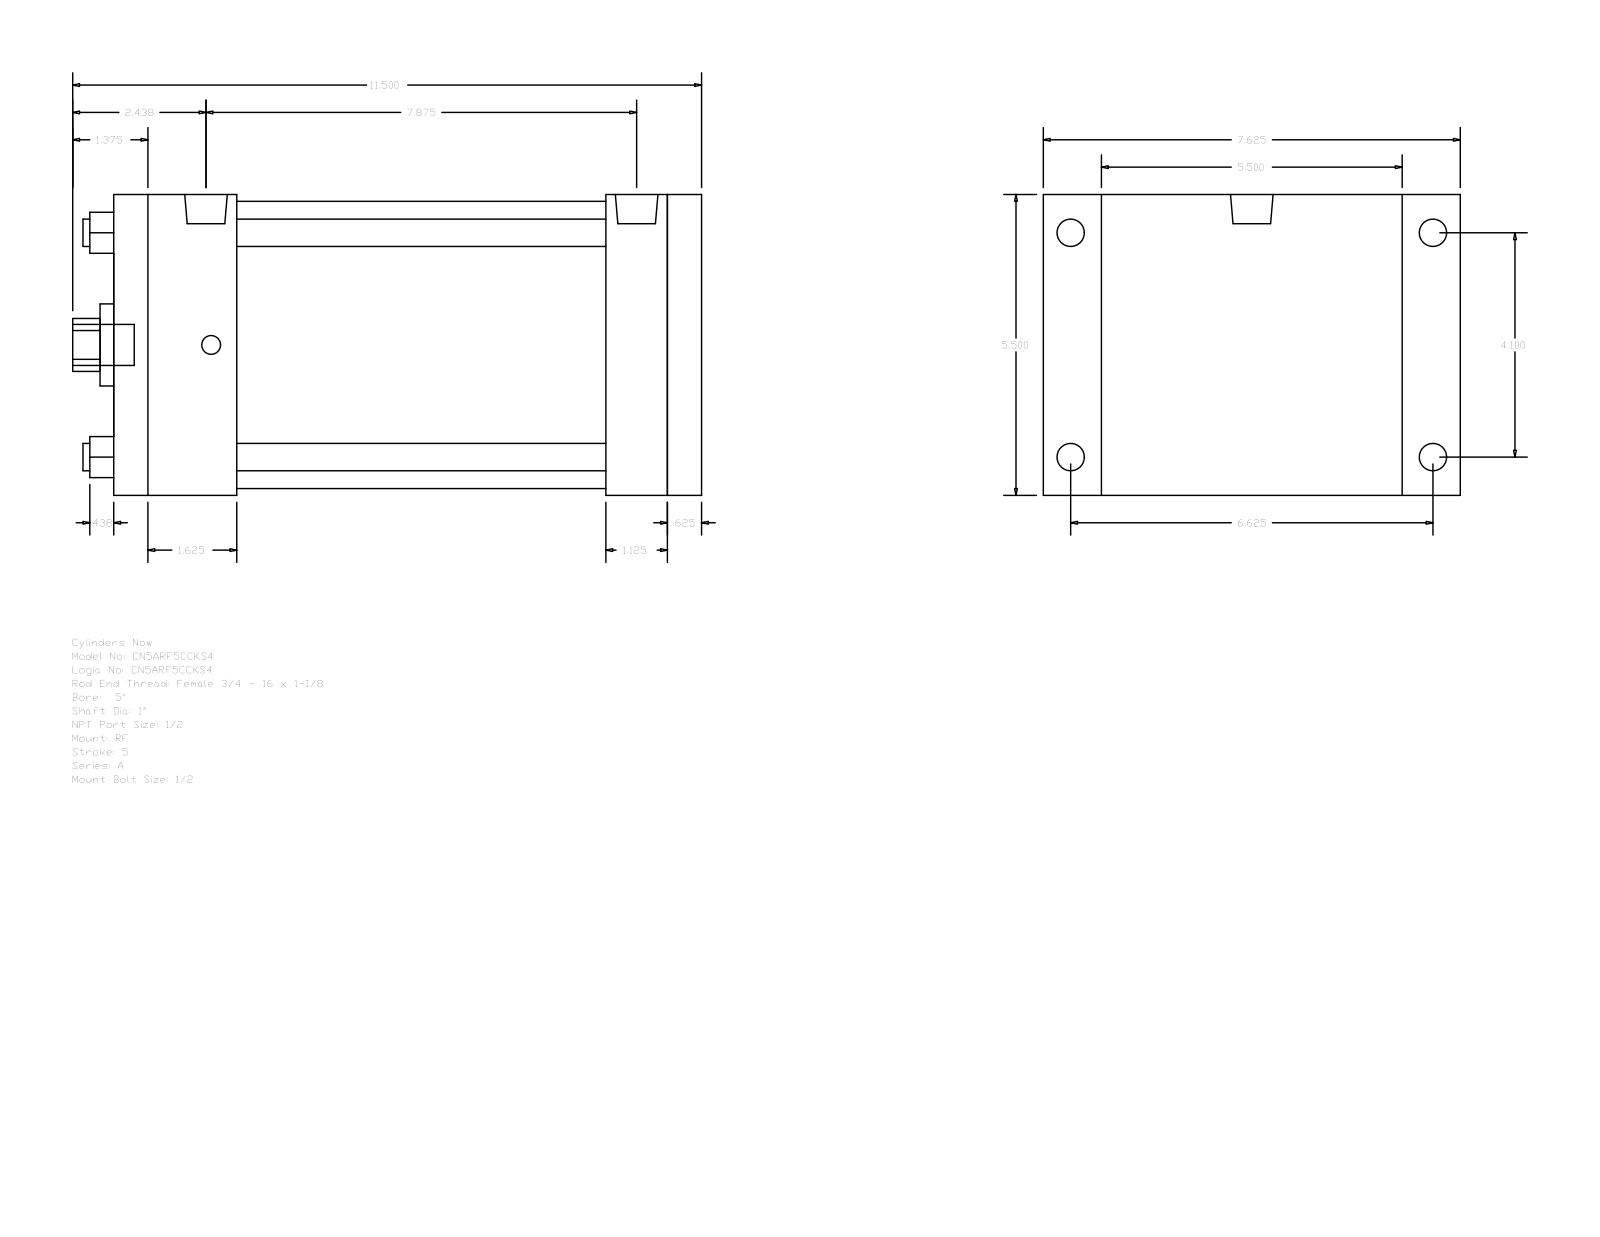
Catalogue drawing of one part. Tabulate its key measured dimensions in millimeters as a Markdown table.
| quantity | value |
| --- | --- |
| part name | A_RF__0500_1 |
| STEP written by | GSSL Pune (CONFIG_CONTROL_DESIGN) |
| units | millimeters |
| bodies | 0 solids, 92 faces (64 planar, 28 cylindrical, 0 other) |
| overall size | 292.1 × 193.68 × 139.7 |
| round holes (diameter × count) | 12.7 × 4, 25.4 × 1, 38.1 × 1, 133.35 × 1 |
| round bosses / shafts (diameter × count) | 12.7 × 4, 8.73 × 4, 19.77 × 2, 19.05 × 1 |
| partial cylindrical surfaces (radius × count) | 12.29 × 1 |
| main face-to-face distances | 139.7, 273.05, 15.87, 257.18, 57.15, 200.03, 215.9, 228.6, 171.45, 28.58 |
| hole center spacings | 73.64, 104.14, 147.28 |
